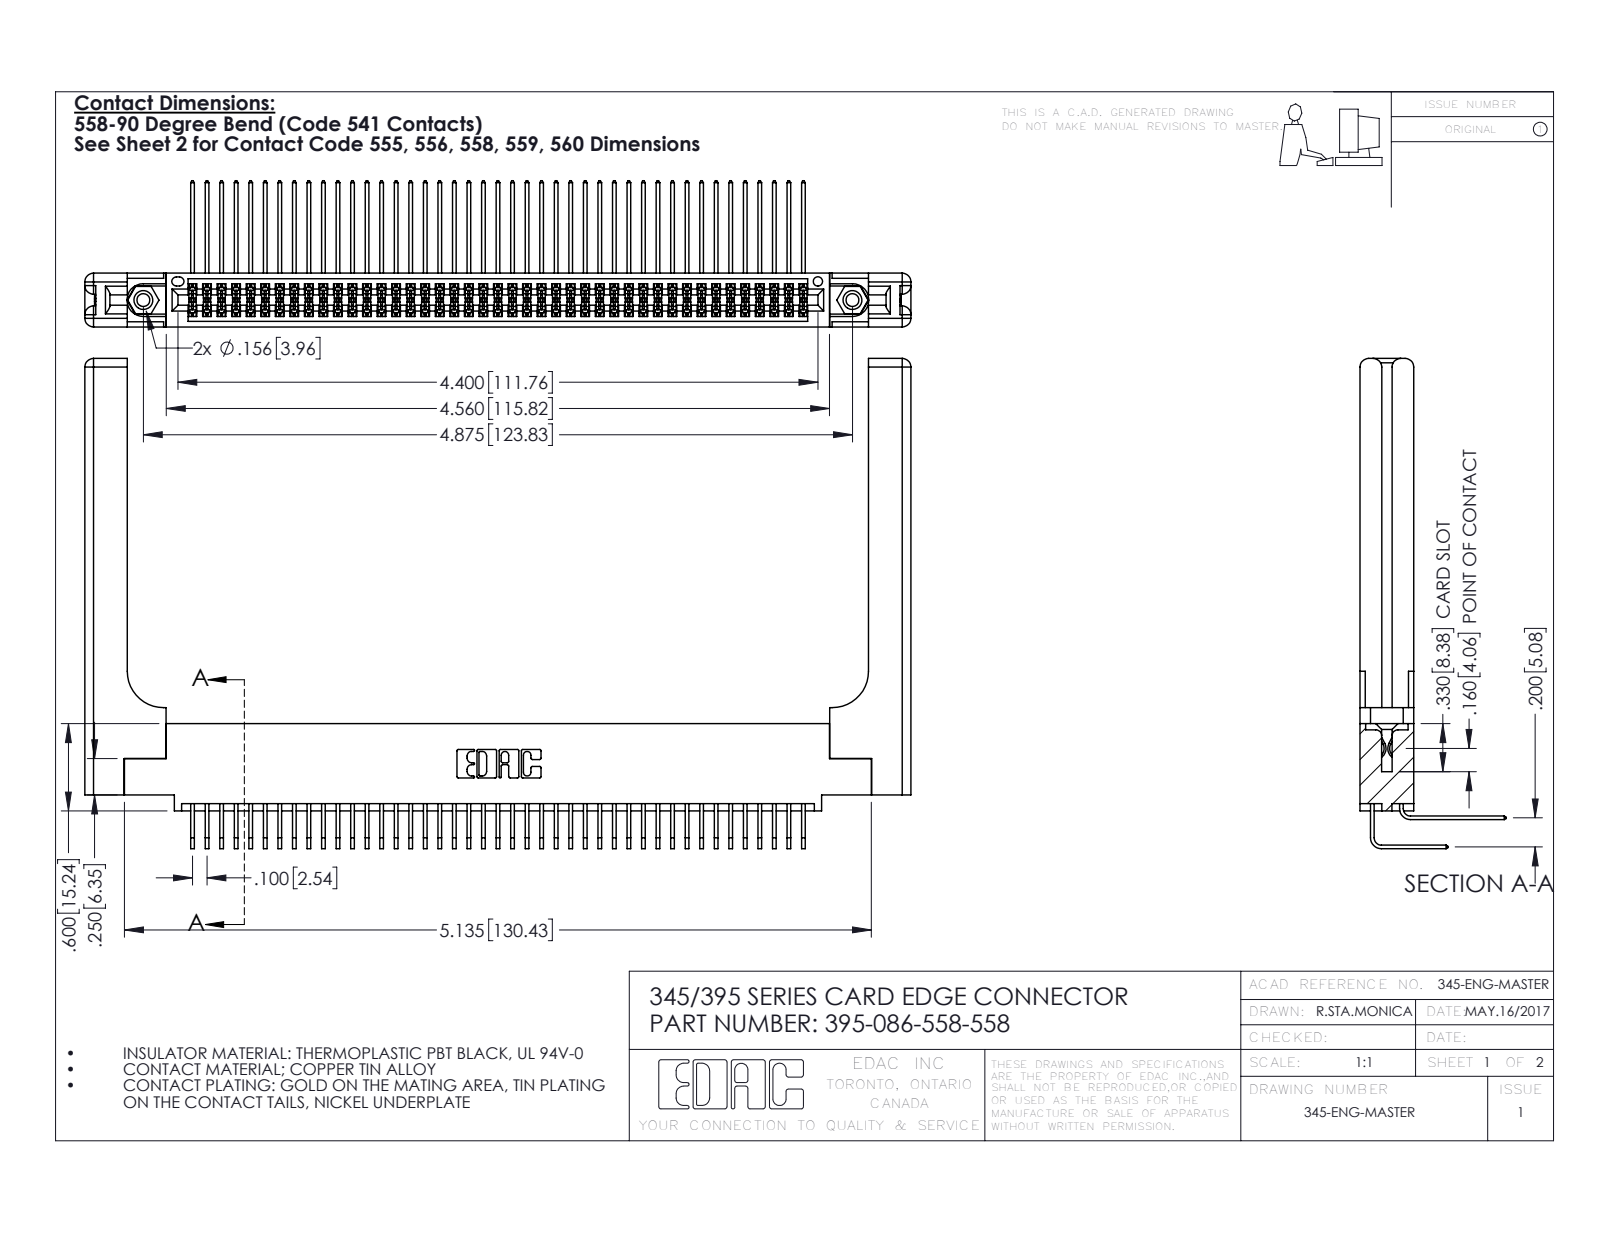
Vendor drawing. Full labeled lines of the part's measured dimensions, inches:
Part name (STEP PRODUCT): 345-250-001_345-250-001-102; 345-292-001_558 Tail - 2; 345-292-001_558 559 Tail - 1; 345-220-058_345-220-058 (+2 more)
STEP written by: SolidWorks 2016 (CONFIG_CONTROL_DESIGN)
Units: inches
Bodies: 91 solids, 4858 faces (3242 planar, 1556 cylindrical, 60 other)
Overall size (bounding box): 5.679 × 3.369 × 1.005
Volume: 1.399 in³ · Surface area: 44.73 in²
Round holes (diameter × count): ⌀0.089 ×2, ⌀0.125 ×2, ⌀0.156 ×2, ⌀0.064 ×1
Round bosses / shafts (diameter × count): ⌀0.155 ×2
Partial cylindrical surfaces — rounded edges, fillets, slot ends (radius × count): R0.006 ×130, R0.01 ×22, R0.06 ×16, R0.007 ×6, R0.031 ×6, R0.026 ×3, R0.014 ×2, R0.019 ×2
Main face-to-face distances: 0.072, 0.298, 0.37, 0.2, 0.098, 0.272, 0.025, 0.225, 0.148, 0.15
Hole centre spacings: 0.27, 4.639, 4.875
